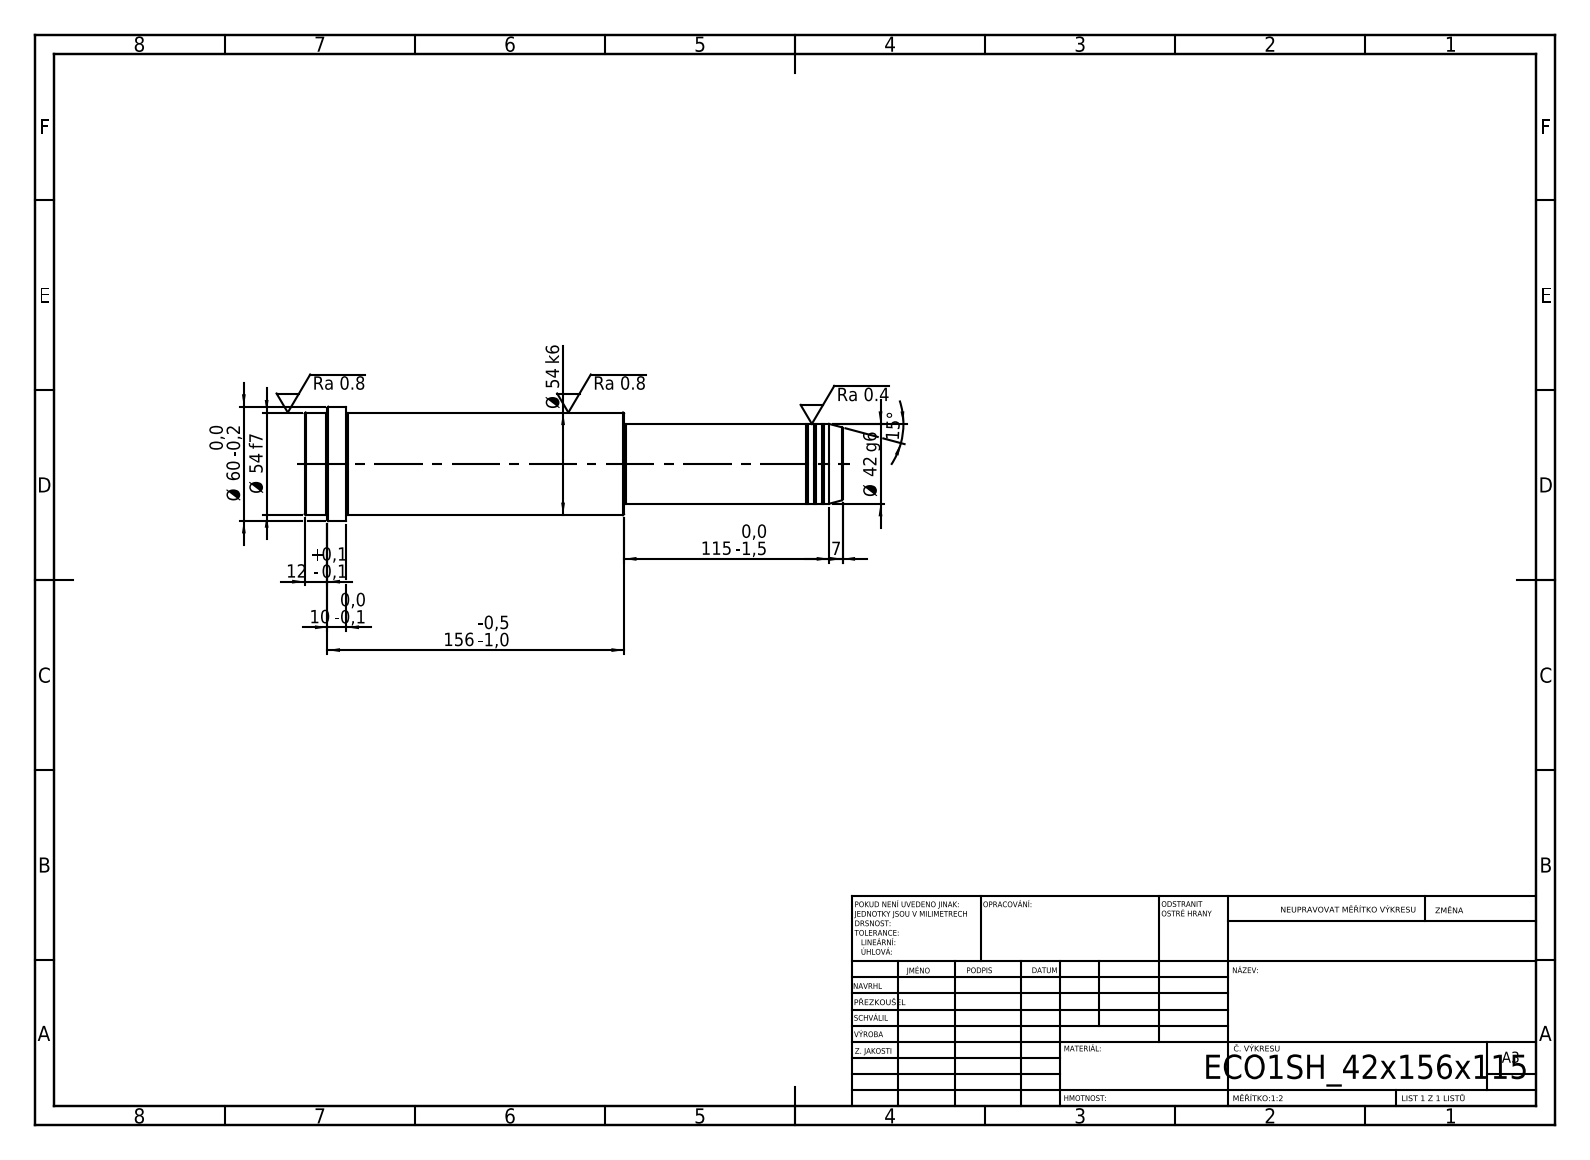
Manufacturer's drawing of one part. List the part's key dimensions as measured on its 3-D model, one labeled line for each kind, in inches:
STEP written by: SolidWorks 2019 (CONFIG_CONTROL_DESIGN)
Units: inches
Bodies: 1 solid, 52 faces (6 planar, 16 cylindrical, 30 other)
Overall size (bounding box): 11.142 × 2.362 × 2.362
Volume: 33.45 in³ · Surface area: 76.93 in²
Round bosses / shafts (diameter × count): ⌀2.362 ×1, ⌀2.126 ×1, ⌀1.654 ×1, ⌀1.614 ×1
Main face-to-face distances: 11.142, 4.528, 6.614, 10.276, 5.748, 0.866, 10.669, 6.142, 0.394, 0.472
